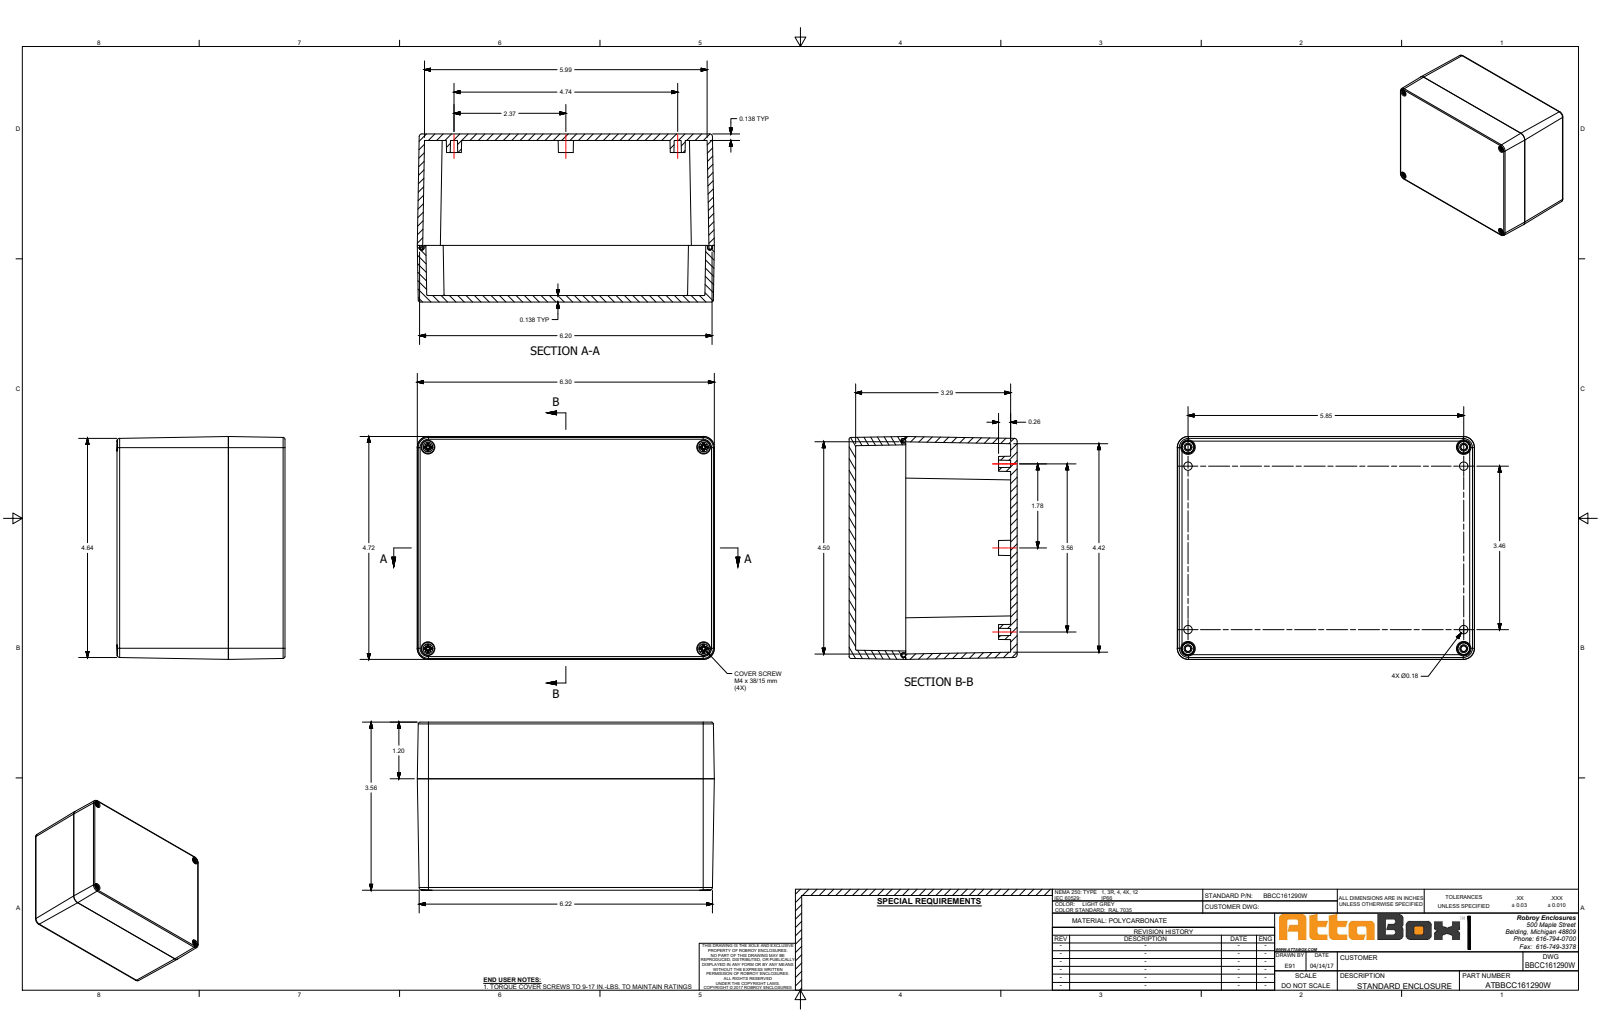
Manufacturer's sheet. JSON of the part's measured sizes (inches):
{"part_name": "BBCC161290W", "step_written_by": "SolidWorks 2018 (AUTOMOTIVE_DESIGN)", "units": "inches", "bodies": {"solids": 11, "faces": 1567, "planar": 591, "cylindrical": 396, "other": 580}, "overall_size": [6.299, 4.724, 3.563], "volume_in3": 18.73, "surface_area_in2": 311.7, "round_holes": [[0.177, 8], [0.128, 4], [0.189, 4], [0.201, 4], [0.276, 4], [0.291, 4], [0.307, 4]], "round_bosses_or_shafts": [[0.268, 4], [0.173, 4], [0.157, 4], [0.13, 4]], "partial_cylinders_radius": [[0.039, 40], [0.02, 30], [0.187, 12], [0.093, 8], [0.059, 4], [0.102, 4], [0.124, 4], [0.14, 4]], "face_to_face_distances": [0.138, 3.425, 0.114, 3.563, 3.287, 4.724, 4.61, 0.177, 4.547, 4.433], "hole_center_spacings": [0.404, 3.868, 5.846, 5.86, 7.01, 3.465, 4.272, 6.796]}
